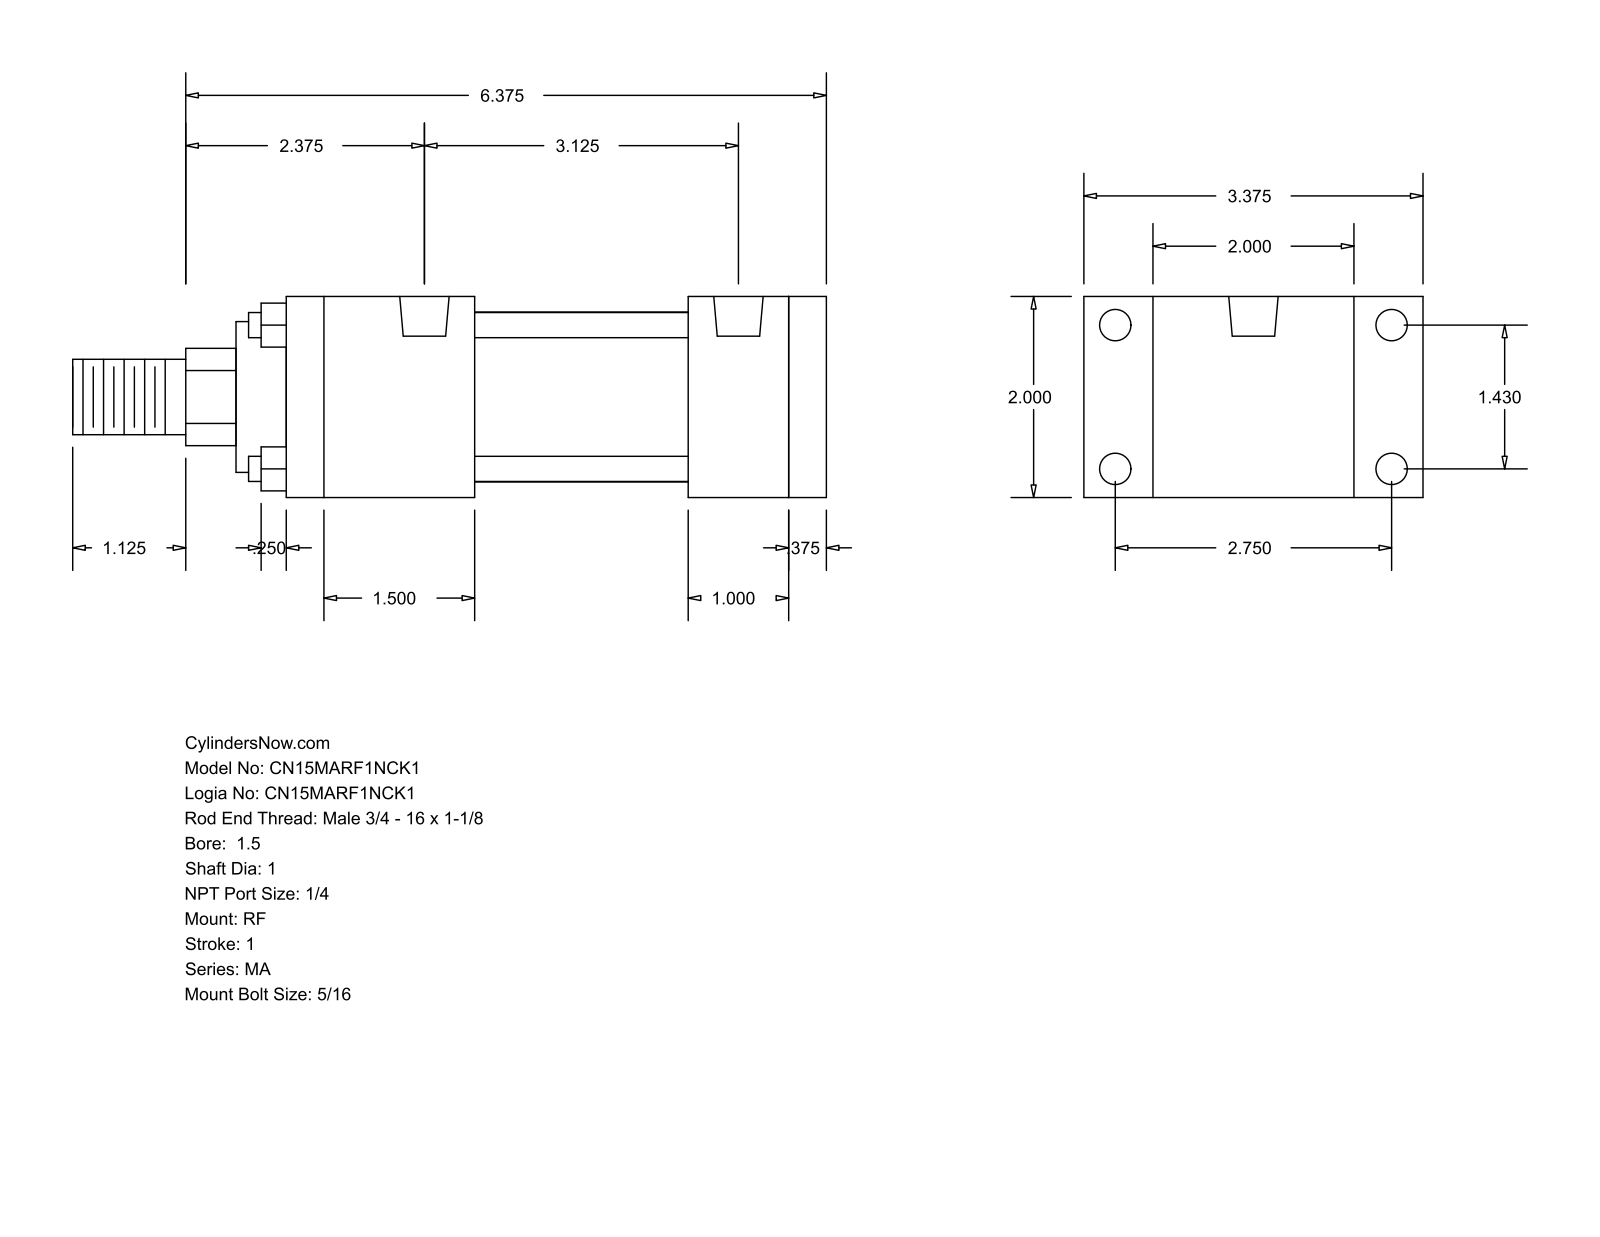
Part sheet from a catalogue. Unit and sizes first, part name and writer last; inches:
Units: inches
Overall size (bounding box): 7.5 × 3.375 × 2
Round holes (diameter × count): ⌀0.313 ×8, ⌀0.492 ×2
Round bosses / shafts (diameter × count): ⌀0.25 ×4, ⌀1.69 ×1, ⌀1.5 ×1, ⌀1 ×1, ⌀0.75 ×1
Partial cylindrical surfaces — rounded edges, fillets, slot ends (radius × count): R0.484 ×1
Main face-to-face distances: 2, 0.375, 4, 2.125, 5, 1, 5.375, 1.375, 1.875, 3.125
Hole centre spacings: 1.43, 2.75, 3.099, 3.125
Bodies: 0 solids, 92 faces (64 planar, 28 cylindrical, 0 other)
Part name (STEP PRODUCT): MA_RF__0150_1
STEP written by: GSSL Pune (CONFIG_CONTROL_DESIGN)
